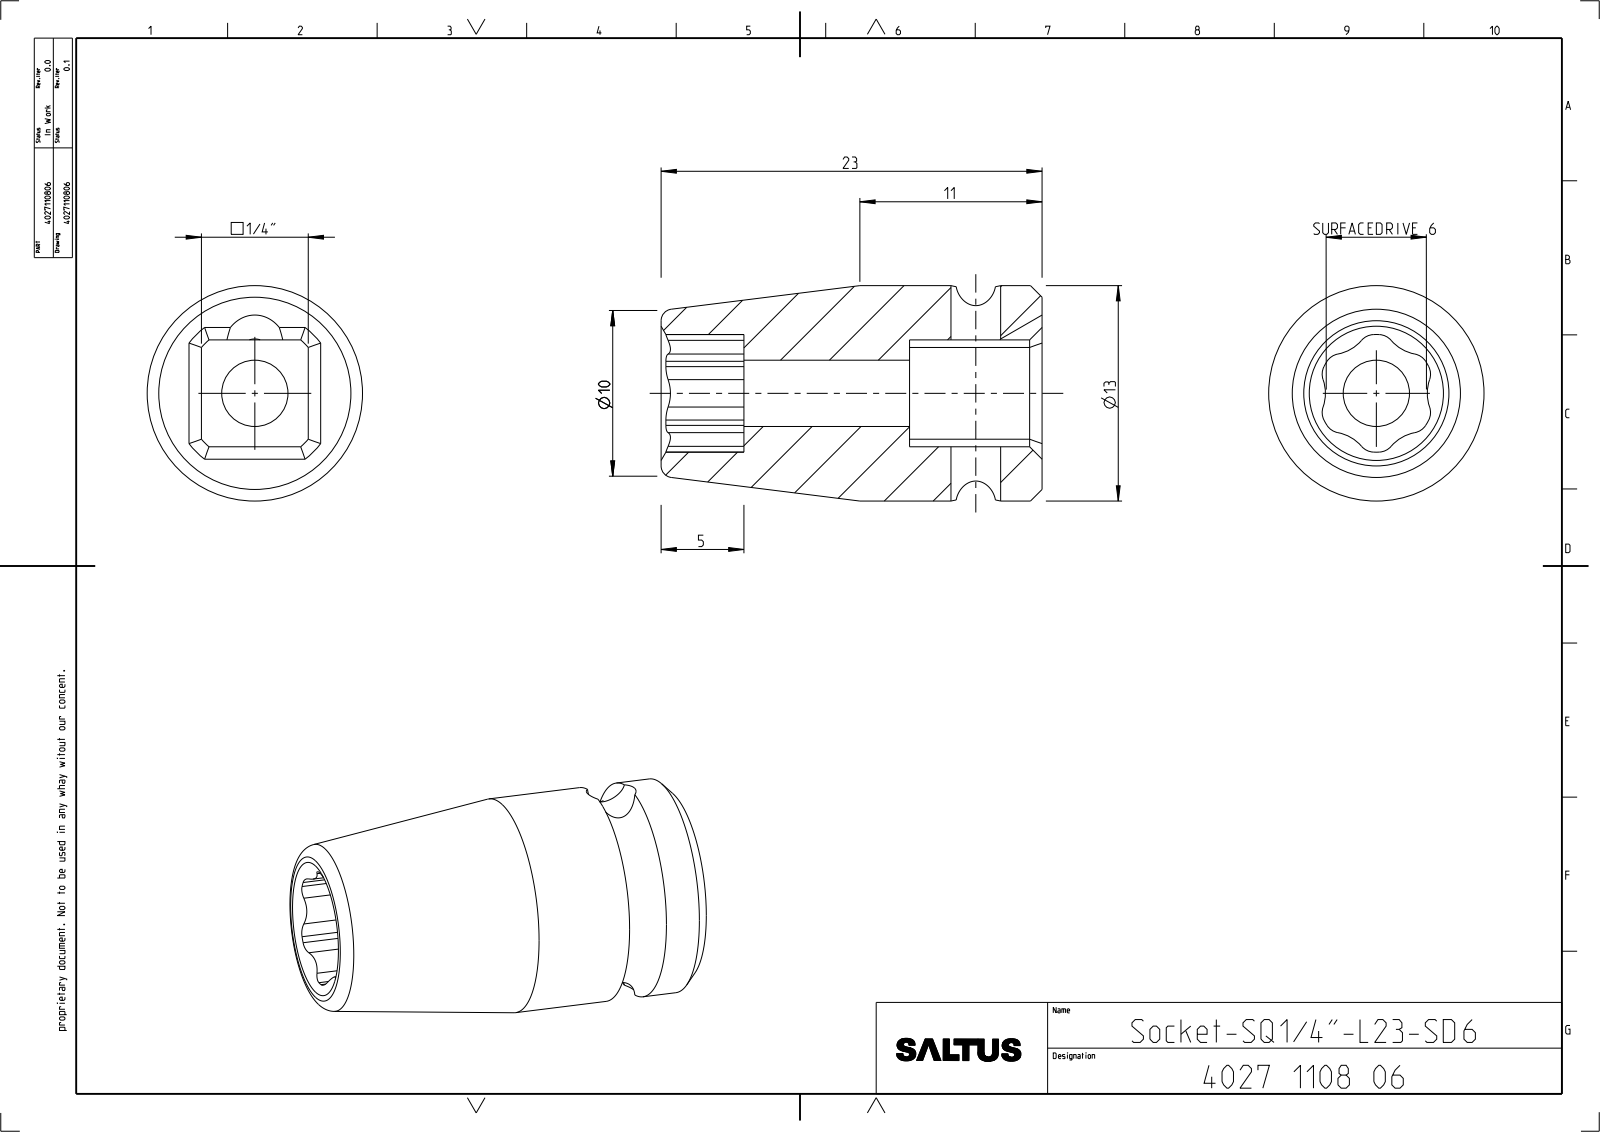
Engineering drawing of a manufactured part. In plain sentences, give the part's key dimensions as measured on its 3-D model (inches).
The part is named "4027110806". Its 3-D file was written by "CREO PARAMETRIC BY PTC INC, 2022414 (CONFIG_CONTROL_DESIGN)". It is 1 solid with 66 faces: 13 planar, 39 cylindrical and 14 other. Overall it measures 0.906 by 0.512 by 0.512 inches. Its volume is 0.119 cubic inches and its surface area 2.342 square inches. Round holes: 1 of diameter 0.118, 1 of diameter 0.157. Round bosses or shafts: 1 of diameter 0.512. Partial cylindrical surfaces (rounded edges, fillets, slot ends): 12 of radius 0.039, 6 of radius 0.098, 1 of radius 0.079, 1 of radius 0.14, 1 of radius 0.167. The main face-to-face distances are 0.254, 0.315, 0.709, 0.394, 0.906, 0.591, 0.197.
